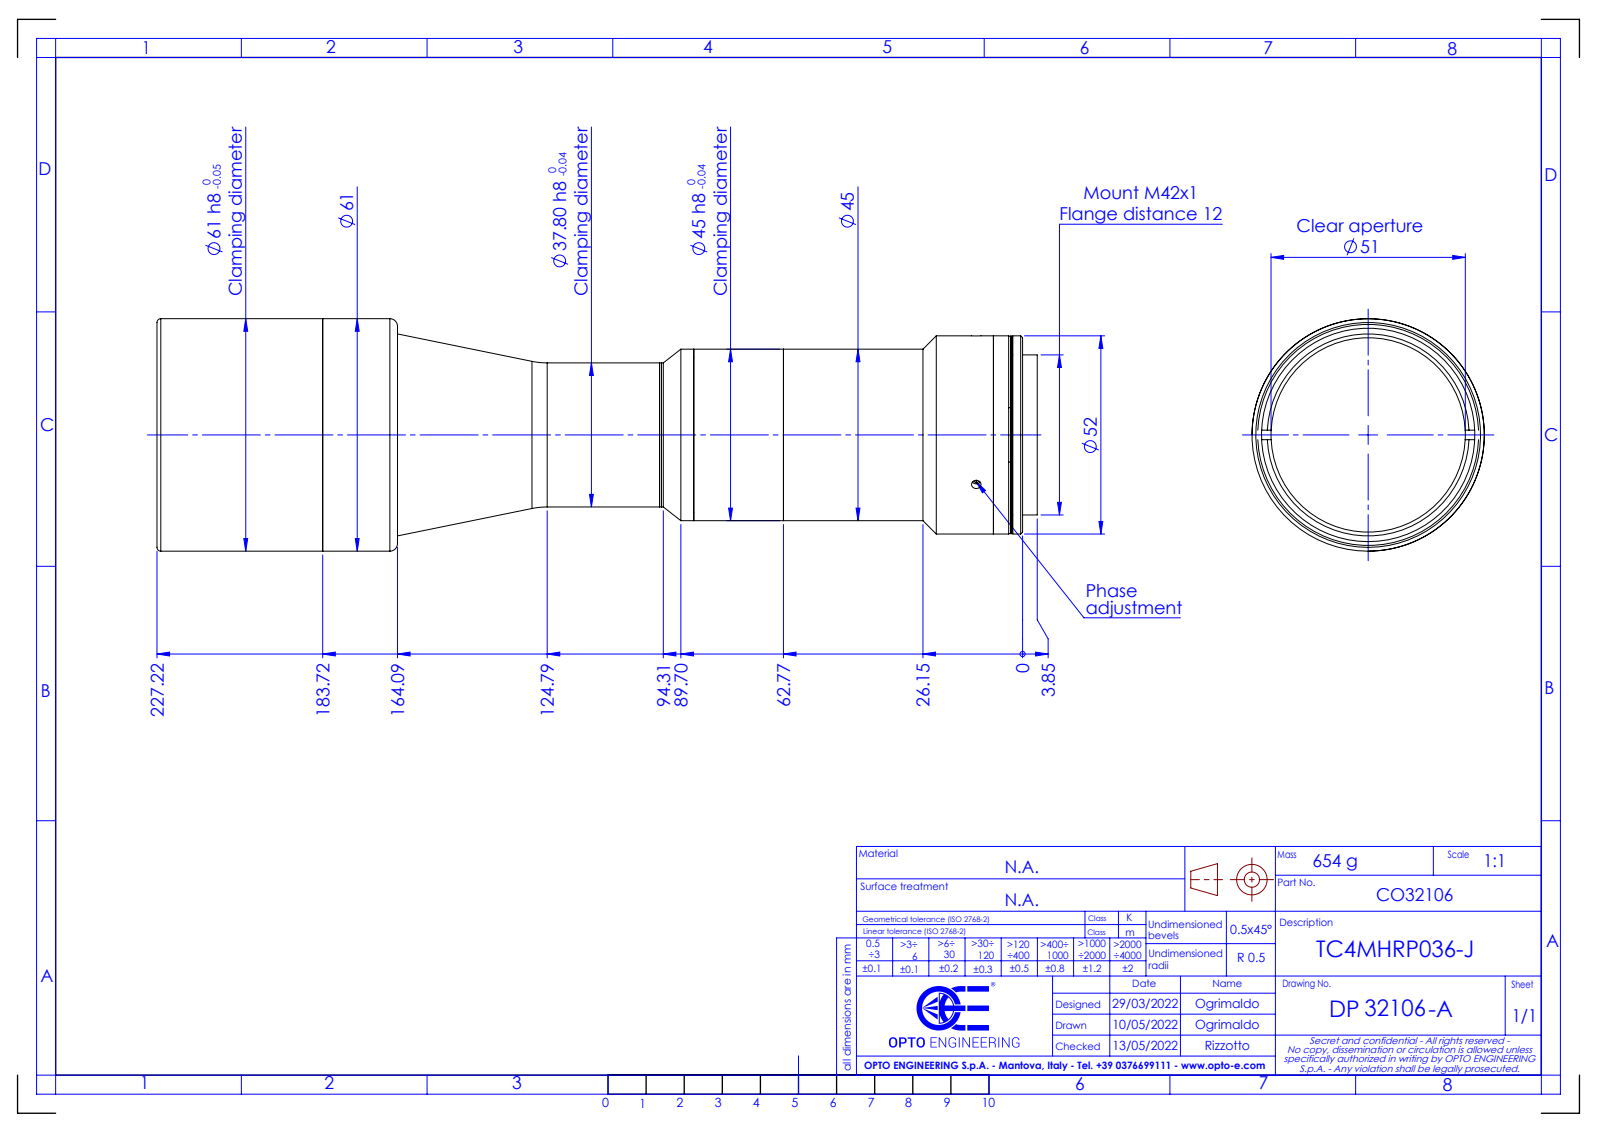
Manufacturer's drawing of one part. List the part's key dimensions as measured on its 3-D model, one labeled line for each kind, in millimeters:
Part name (STEP PRODUCT): DP32106-A_TC4MHRP036-J
STEP written by: SolidWorks 2021 (CONFIG_CONTROL_DESIGN)
Units: millimetres
Bodies: 0 solids, 98 faces (28 planar, 48 cylindrical, 22 other)
Overall size (bounding box): 231.06 × 61 × 61
Round holes (diameter × count): ⌀2.5 ×3, ⌀38 ×1, ⌀41 ×1, ⌀51 ×1, ⌀53 ×1, ⌀56 ×1
Round bosses / shafts (diameter × count): ⌀61 ×1, ⌀52 ×1, ⌀51.8 ×1, ⌀45 ×1, ⌀42 ×1, ⌀37.8 ×1
Main face-to-face distances: 87.16, 92.25, 5.09, 91.16, 4, 1.09, 94.81, 7.65, 3.65, 2.56
